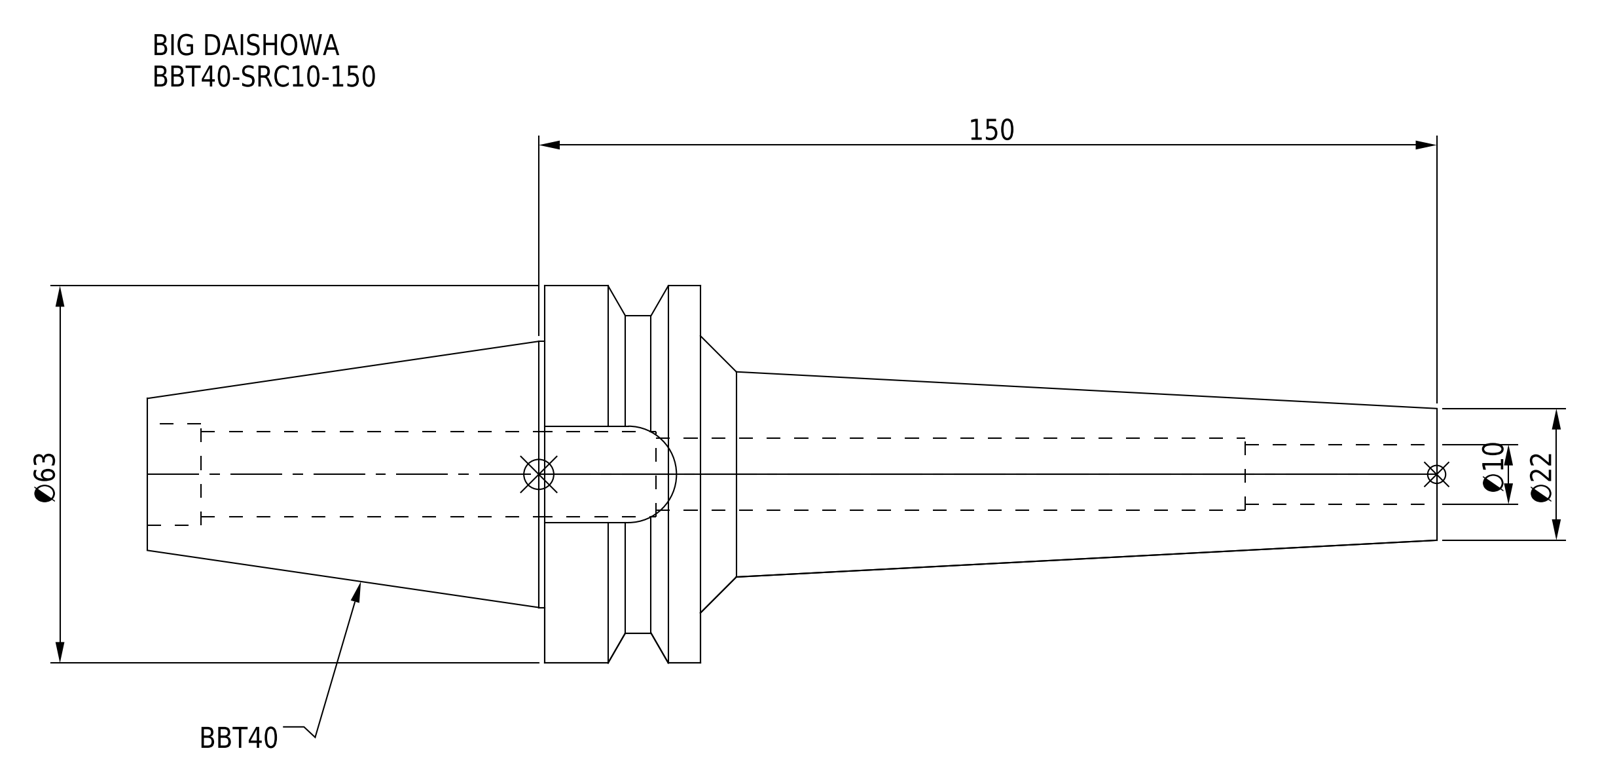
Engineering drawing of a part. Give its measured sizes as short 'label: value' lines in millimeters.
name: BBT40-SRC10-150
written by: CREO PARAMETRIC BY PTC INC, 2016380 (AUTOMOTIVE_DESIGN)
unit: mm
bodies: 1 solid, 43 faces (13 planar, 20 cylindrical, 10 other)
size: 215.4 × 63 × 63
volume: 189 429 mm³; area: 37 368 mm²
holes: 1× ⌀10, 1× ⌀12, 1× ⌀14.2, 1× ⌀17
bosses: 1× ⌀63, 1× ⌀53, 1× ⌀44.45
rounds: 1× R8.05
face distances: 26, 45, 123, 149, 215.4, 92.4, 66.4, 16.1, 206.4, 83.4
